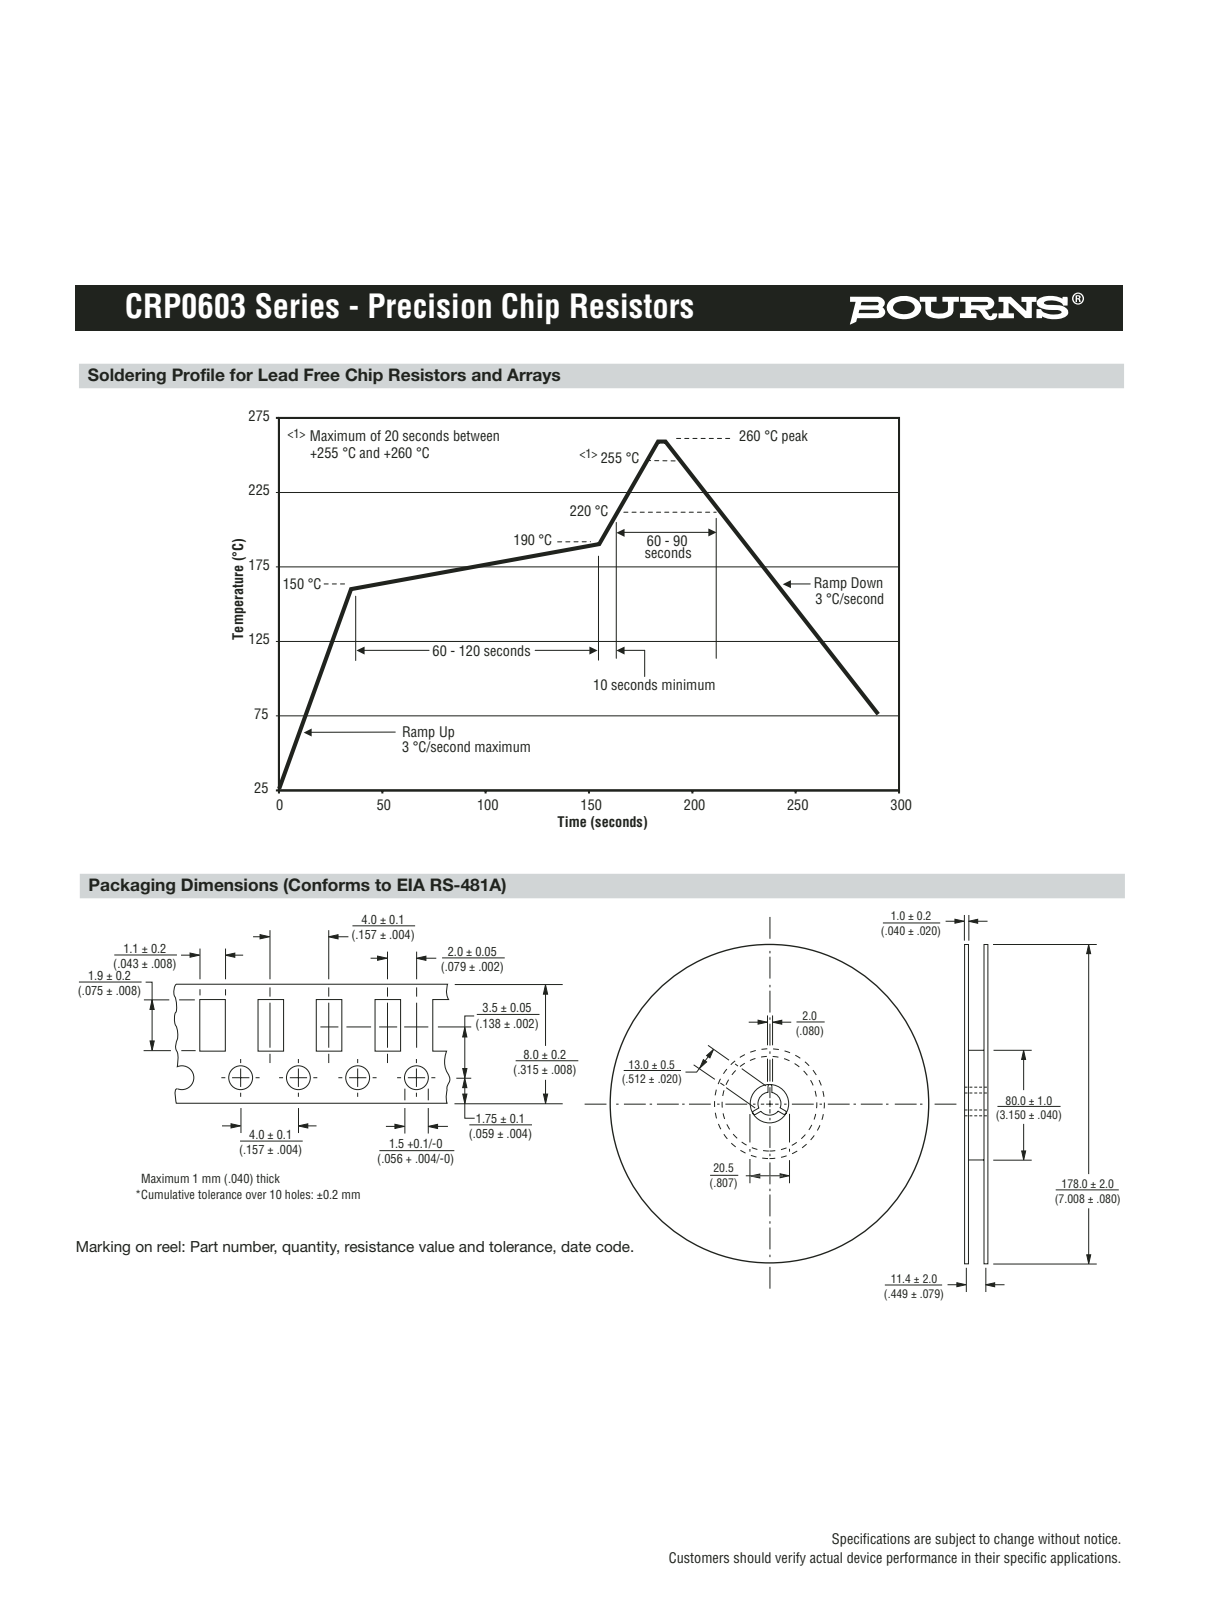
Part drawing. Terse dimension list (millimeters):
name: CR2512
written by: PRO/ENGINEER BY PARAMETRIC TECHNOLOGY CORPORATION, 2010100 (CONFIG_CONTROL_DESIGN)
unit: mm
bodies: 1 solid, 14 faces (14 planar, 0 cylindrical, 0 other)
size: 1.6 × 0.8 × 0.45
volume: 0.552 mm³; area: 5 mm²
face distances: 0.43, 0.8, 0.45, 0.41, 1.6, 0.4, 1.2
